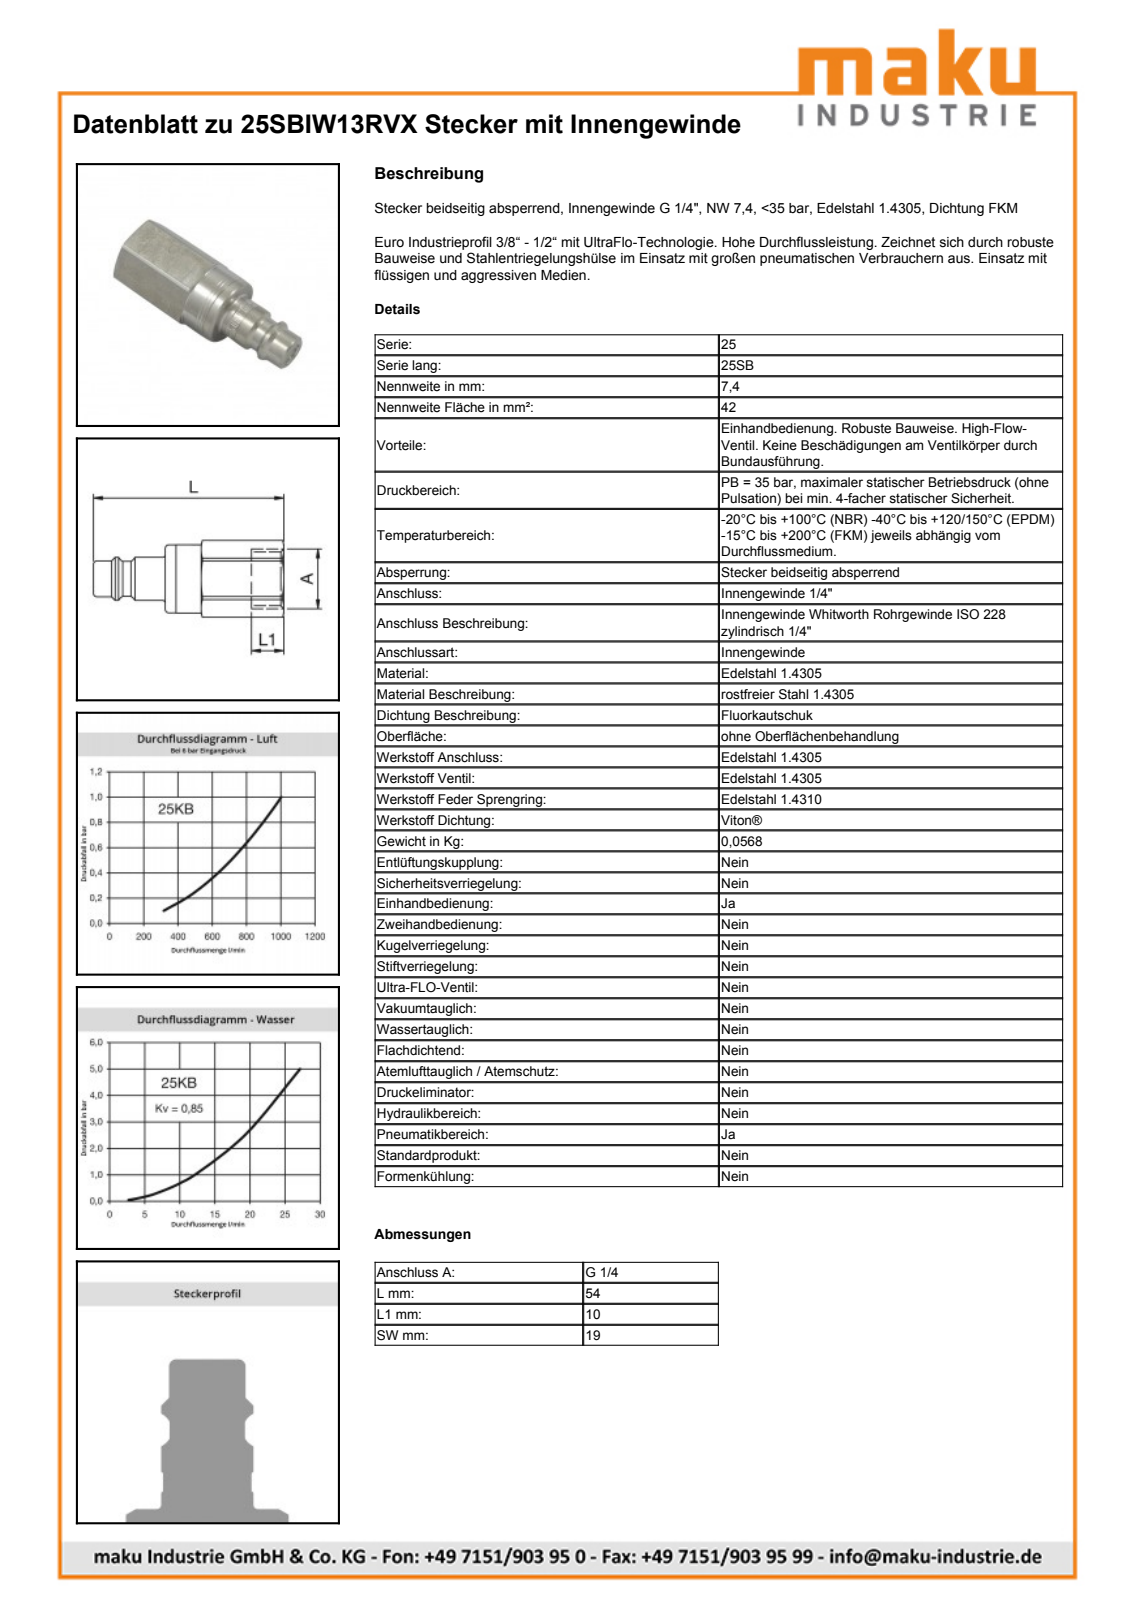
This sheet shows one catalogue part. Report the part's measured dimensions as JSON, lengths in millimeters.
{"part_name": "D108505", "step_written_by": "Autodesk Inventor 2013 (AUTOMOTIVE_DESIGN)", "units": "millimeters", "bodies": {"solids": 1, "faces": 44, "planar": 14, "cylindrical": 17, "other": 13}, "overall_size": [54, 21.29, 20.98], "volume_mm3": 11510, "surface_area_mm2": 4281, "round_holes": [[11.45, 1], [15.6, 1]], "round_bosses_or_shafts": [[19, 1], [18.95, 1], [15.24, 1], [14.5, 1], [12, 1], [9.9, 1], [9.75, 1]], "partial_cylinders_radius": [[10.7, 1]], "face_to_face_distances": [19.6, 19.62, 10, 24, 34, 20, 44, 54, 3, 23]}
